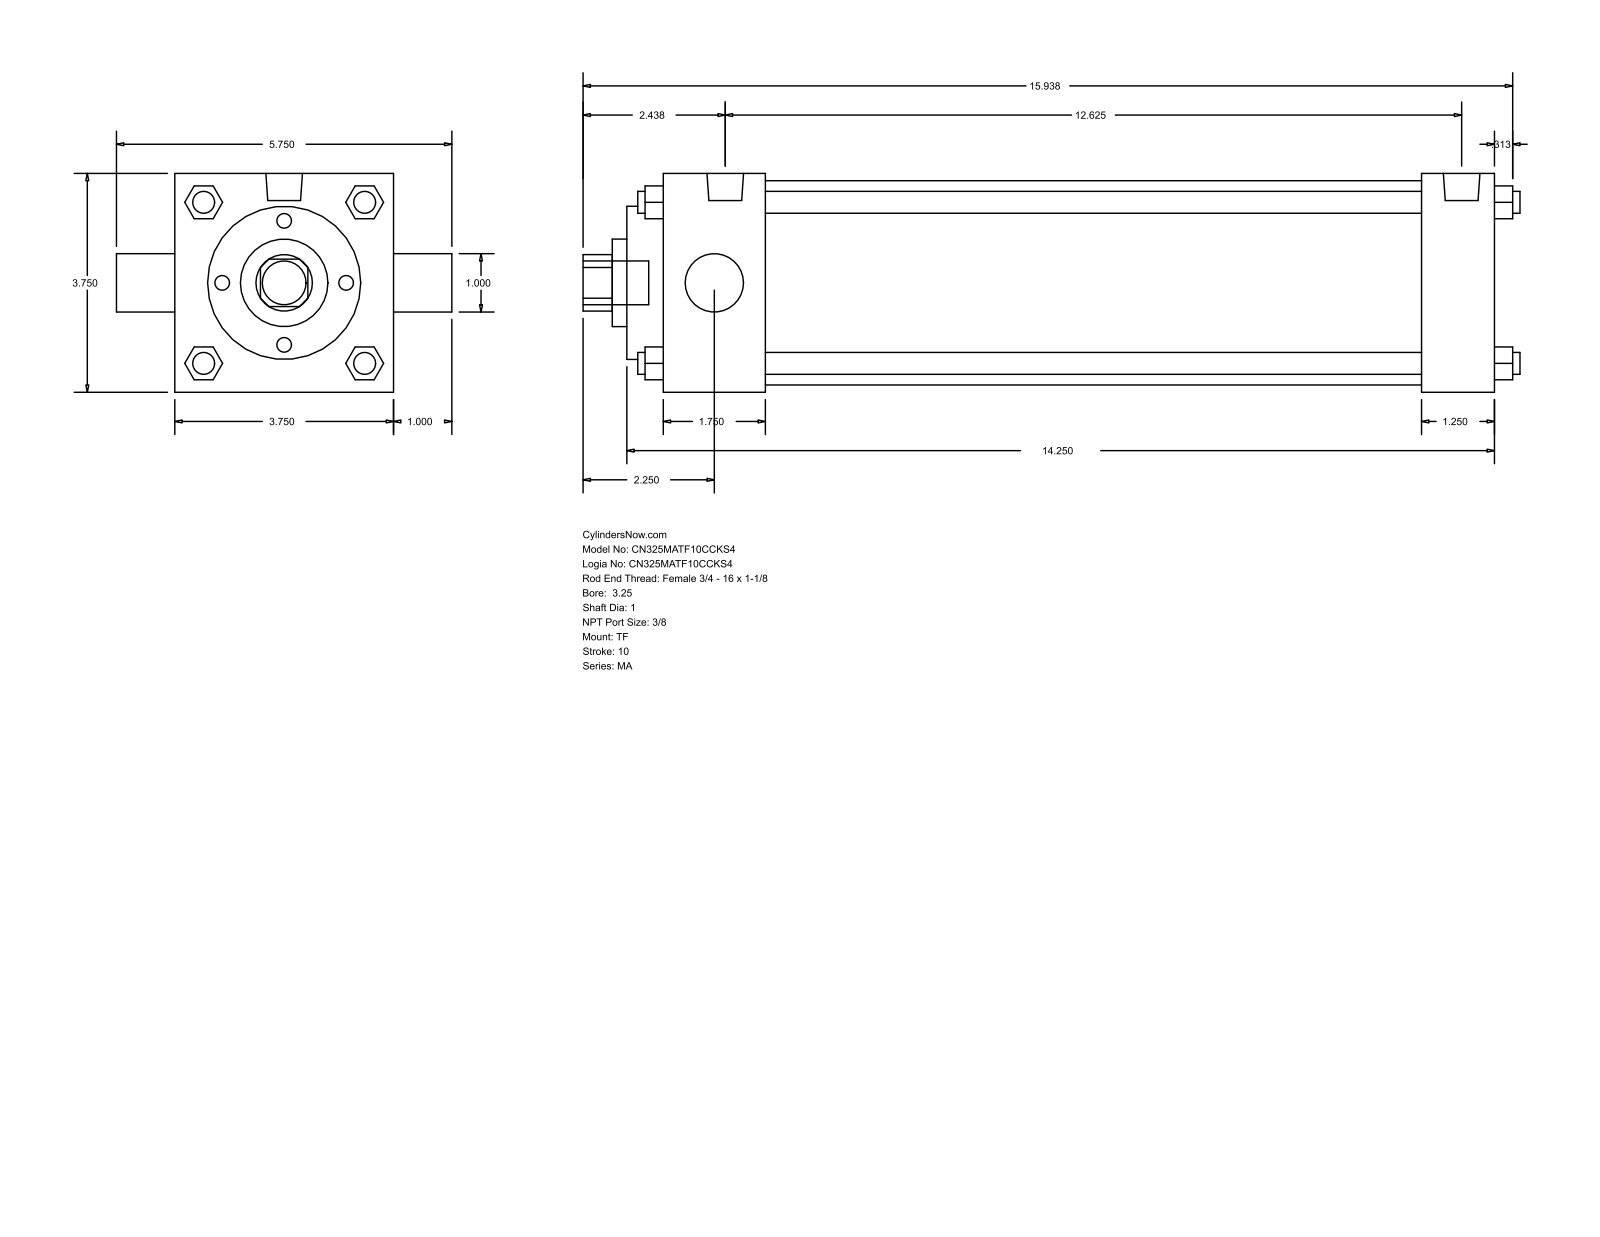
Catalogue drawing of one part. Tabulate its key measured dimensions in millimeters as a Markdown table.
| quantity | value |
| --- | --- |
| part name | MA_TF__0325_1 |
| STEP written by | GSSL Pune (CONFIG_CONTROL_DESIGN) |
| units | millimeters |
| bodies | 0 solids, 122 faces (93 planar, 29 cylindrical, 0 other) |
| overall size | 407.99 × 146.05 × 95.25 |
| round holes (diameter × count) | 25.4 × 2, 38.1 × 1, 66.67 × 1, 88.9 × 1 |
| round bosses / shafts (diameter × count) | 9.53 × 4, 11.11 × 3, 15.93 × 2, 19.05 × 1 |
| partial cylindrical surfaces (radius × count) | 12.29 × 1 |
| main face-to-face distances | 95.24, 361.96, 15.87, 44.46, 330.2, 285.74, 317.5, 31.76, 60.33, 346.07 |
